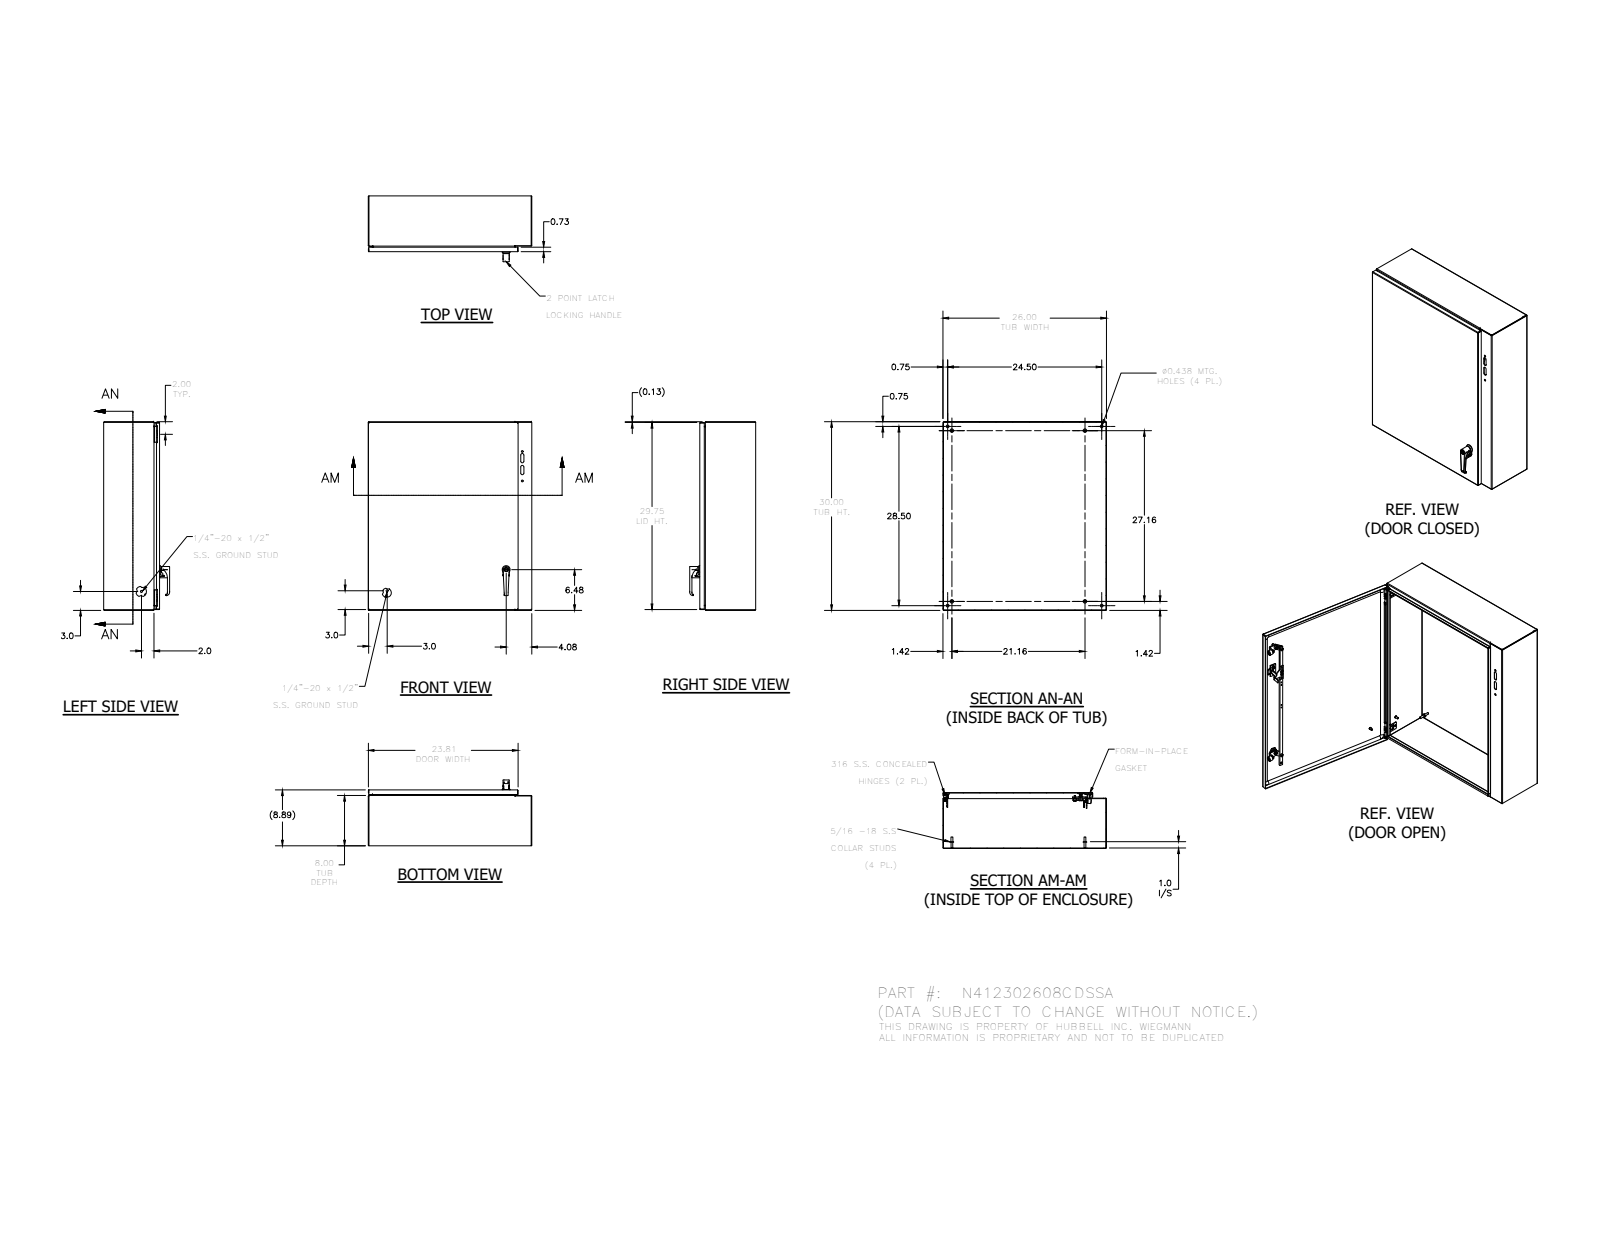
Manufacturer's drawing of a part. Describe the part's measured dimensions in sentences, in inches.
The part is named "N412302608CDSSA". Its 3-D file was written by "SolidWorks 2019 (AUTOMOTIVE_DESIGN)". It is 61 solids with 2090 faces: 817 planar, 740 cylindrical and 533 other. Overall it measures 30 by 26 by 10.481 inches. Its volume is 221.1 cubic inches and its surface area 5 623 square inches. Round holes: 6 of diameter 0.145, 4 of diameter 0.093, 4 of diameter 0.152, 4 of diameter 0.156, 4 of diameter 0.167, 4 of diameter 0.172, 4 of diameter 0.187, 4 of diameter 0.437, 3 of diameter 0.32, 2 of diameter 0.196, 2 of diameter 0.211, 2 of diameter 0.22. Round bosses or shafts: 12 of diameter 0.25, 8 of diameter 0.3, 4 of diameter 0.563, 4 of diameter 0.437, 4 of diameter 0.36, 4 of diameter 0.32, 4 of diameter 0.256, 4 of diameter 0.19. Partial cylindrical surfaces (rounded edges, fillets, slot ends): 38 of radius 0.02, 30 of radius 0.012, 26 of radius 0.031, 26 of radius 0.05, 25 of radius 0.125, 18 of radius 0.016, 16 of radius 0.025, 16 of radius 0.105. The main face-to-face distances are 0.074, 8.812, 8.738, 8.886, 29.926, 0.074, 7.926, 0.886, 26, 25.852. The hole center spacings are 26, 0.66, 0.5, 0.656, 1.307, 1.965, 25.34, 26.66.
